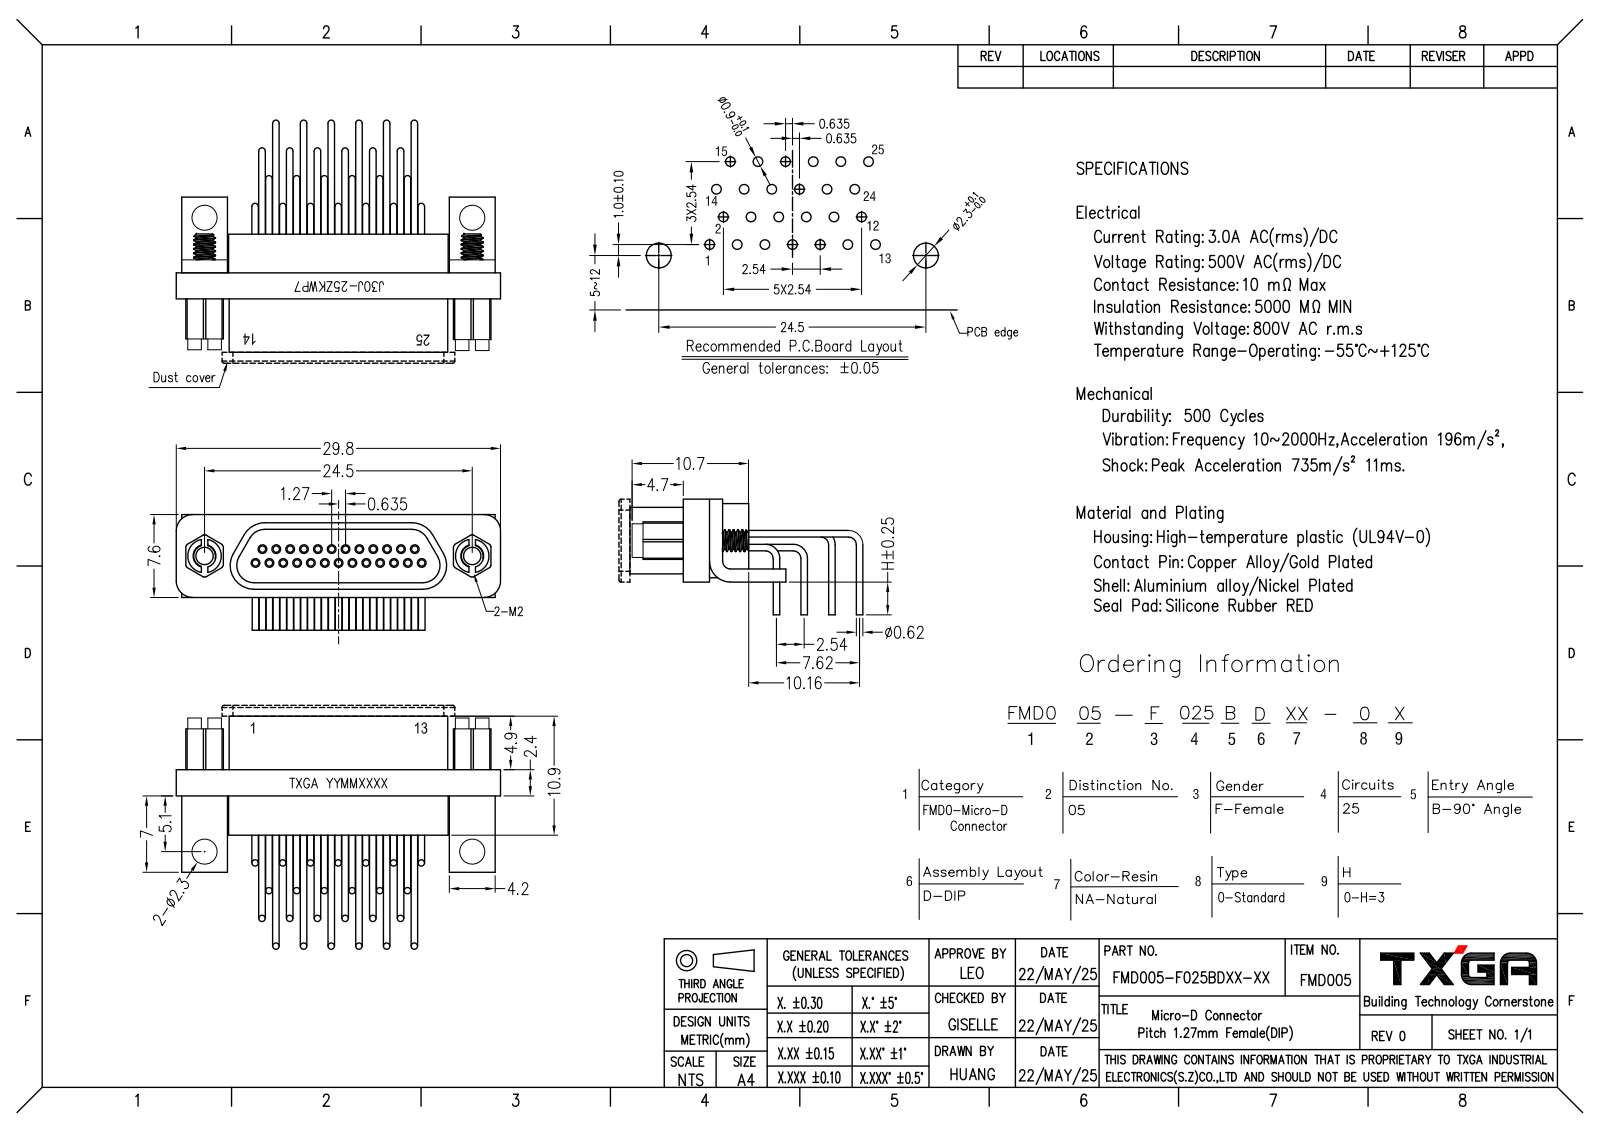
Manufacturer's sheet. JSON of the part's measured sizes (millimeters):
{"part_name": "FMD005-F025BDRD-00", "step_written_by": "SolidWorks 2021 (CONFIG_CONTROL_DESIGN)", "units": "millimeters", "bodies": {"solids": 1, "faces": 1420, "planar": 651, "cylindrical": 346, "other": 423}, "overall_size": [29.8, 21.36, 10.6], "volume_mm3": 1453, "surface_area_mm2": 2625, "round_holes": [[0.6, 25], [1.6, 2], [1.8, 2], [2.3, 2]], "round_bosses_or_shafts": [[0.8, 25], [0.6, 25], [3.1, 2], [2, 2]], "partial_cylinders_radius": [[0.3, 12], [1.5, 4], [1.6, 4], [1.8, 4], [2.2, 4], [1.15, 2], [0.7, 1], [1.9, 1]], "face_to_face_distances": [6, 0.6, 0.75, 1.35, 5.5, 6.25, 6.85, 0.95, 0.4, 7.2], "hole_center_spacings": [1.27, 2.2, 2.54, 3.36, 3.81, 5.08, 6.35, 7.62]}
